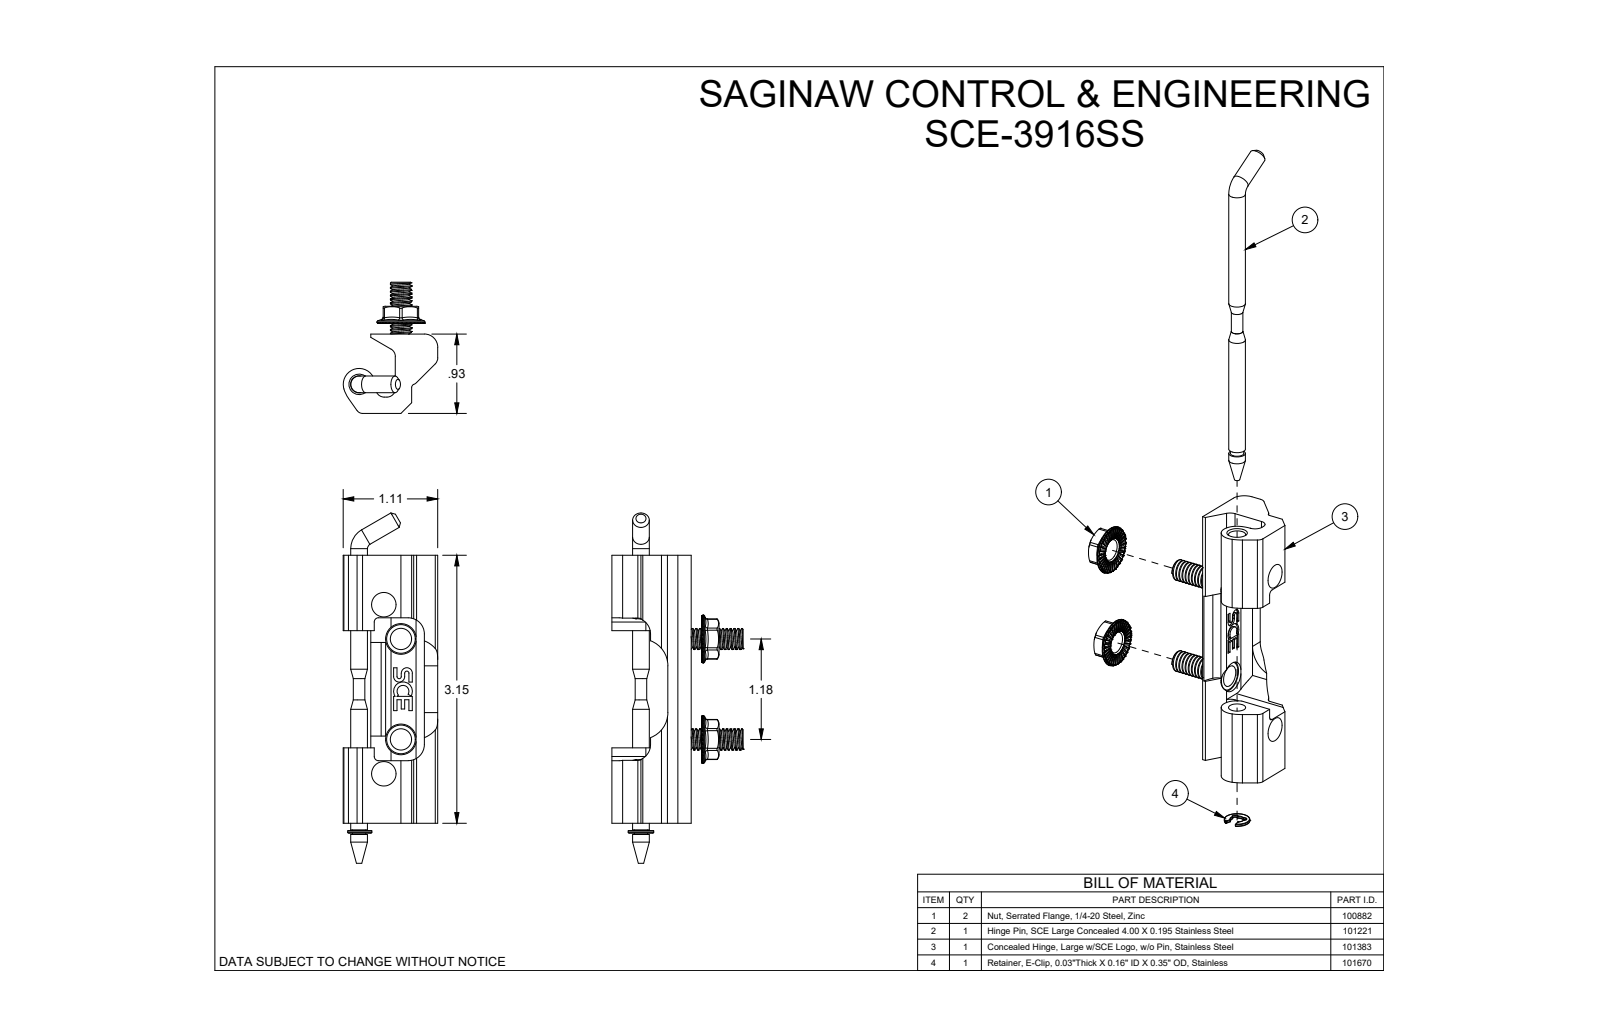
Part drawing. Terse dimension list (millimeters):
name: SCE-3916SS
written by: SolidWorks 2019 (CONFIG_CONTROL_DESIGN)
unit: mm
bodies: 7 solids, 683 faces (232 planar, 110 cylindrical, 341 other)
size: 104.6 × 39.2 × 28.2
volume: 20 450 mm³; area: 12 820 mm²
holes: 2× ⌀6.4, 2× ⌀6.4, 2× ⌀9.1, 1× ⌀1, 1× ⌀5.1
bosses: 2× ⌀14.3, 2× ⌀8.6, 2× ⌀6.3, 2× ⌀5, 1× ⌀7.6, 1× ⌀4, 1× ⌀3.5
rounds: 12× R0.7, 3× R0.3, 3× R2.5, 3× R2.5, 2× R0.1, 2× R0.6, 2× R0.8, 2× R1.3
face distances: 23.7, 80, 12.7, 4.9, 18.7, 61.3, 3.6, 20.1, 7.8, 3.2
hole spacings: 15, 30
